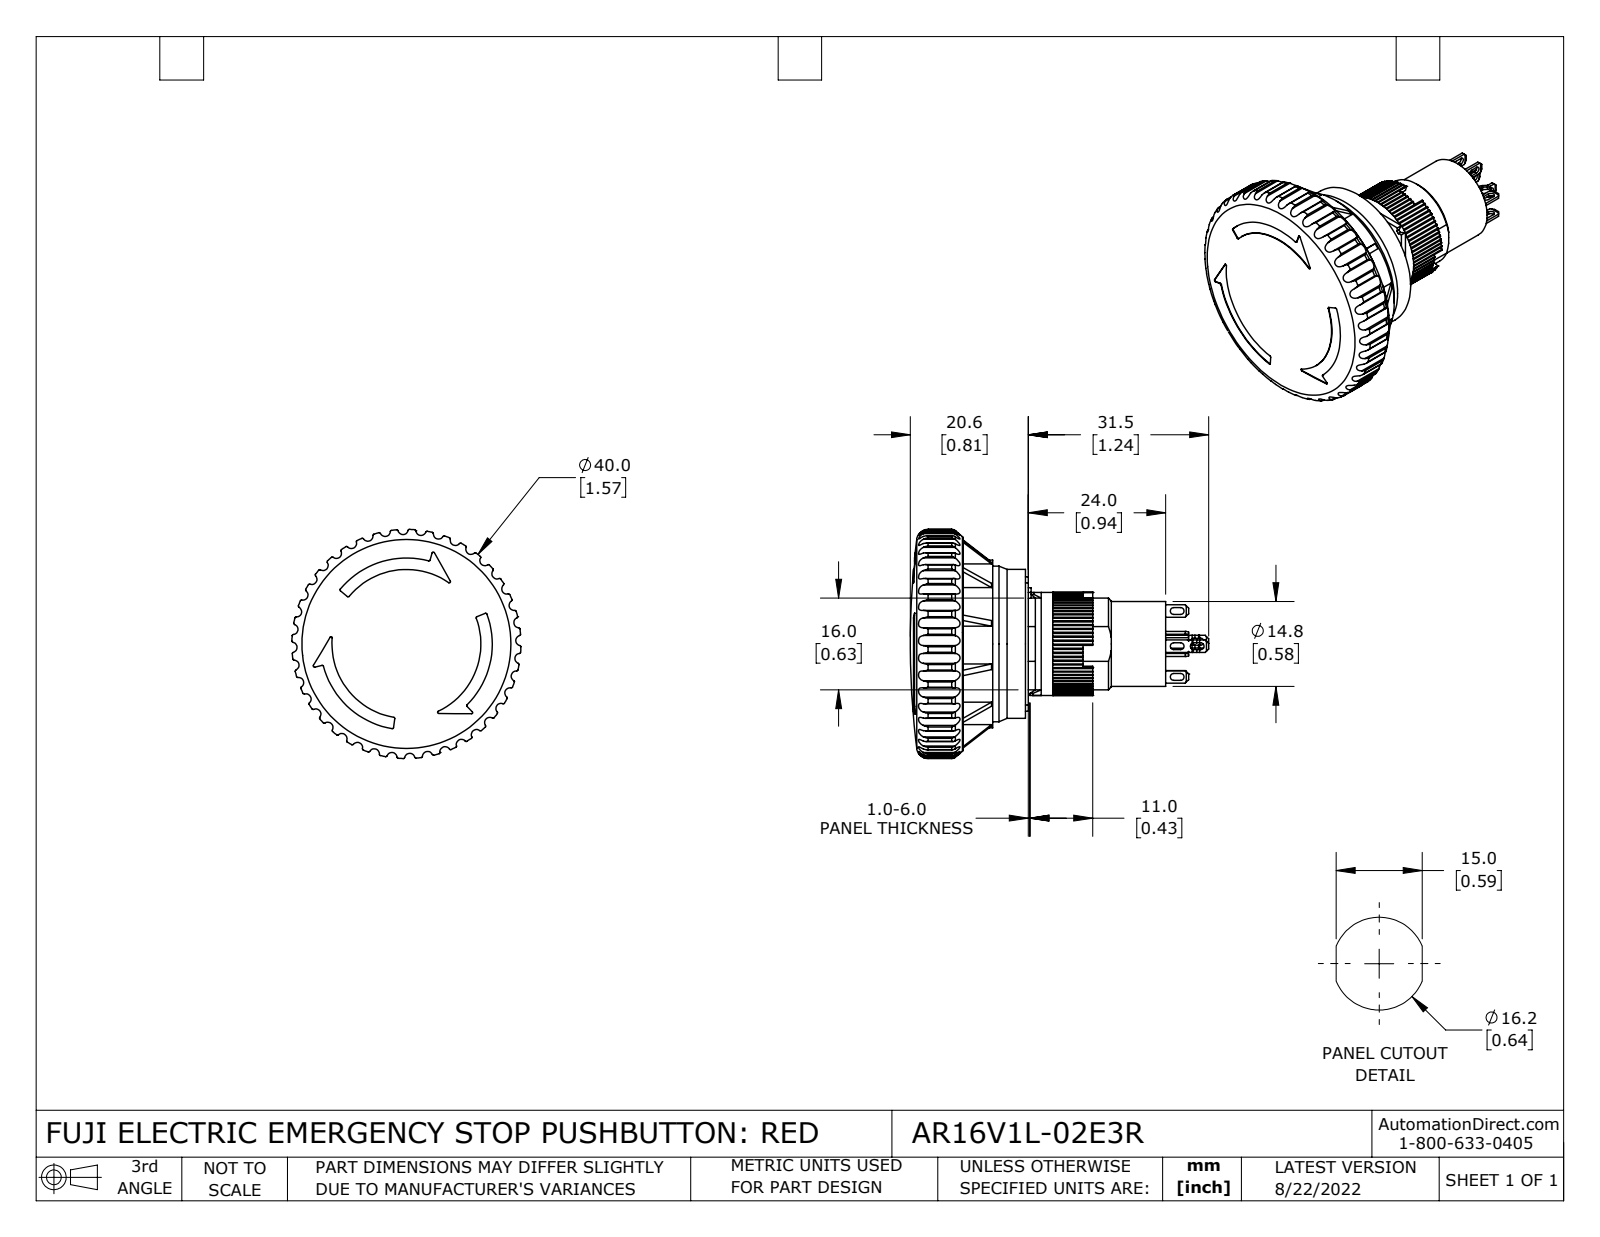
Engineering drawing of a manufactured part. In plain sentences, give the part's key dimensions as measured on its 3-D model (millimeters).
The part is named "AR16V1L-02E3R". Its 3-D file was written by "SolidWorks 2021 (CONFIG_CONTROL_DESIGN)". It is 7 solids with 1081 faces: 547 planar, 438 cylindrical and 96 other. Overall it measures 52.1 by 40 by 40 millimeters. Its volume is 15 800 cubic millimeters and its surface area 12 370 square millimeters. Round holes: 1 of diameter 14.8, 1 of diameter 16, 1 of diameter 18, 1 of diameter 27.2, 1 of diameter 36.4. Round bosses or shafts: 1 of diameter 29.3, 1 of diameter 26, 1 of diameter 21.8, 1 of diameter 6. Partial cylindrical surfaces (rounded edges, fillets, slot ends): 80 of radius 0.2, 80 of radius 0.3, 40 of radius 0.9, 16 of radius 0.6, 8 of radius 0.5, 4 of radius 0.3, 4 of radius 0.7, 2 of radius 1. The main face-to-face distances are 1, 10.7, 13.5, 2.7, 0.5, 1.8, 21.7, 12.4, 2.3, 1.2.
